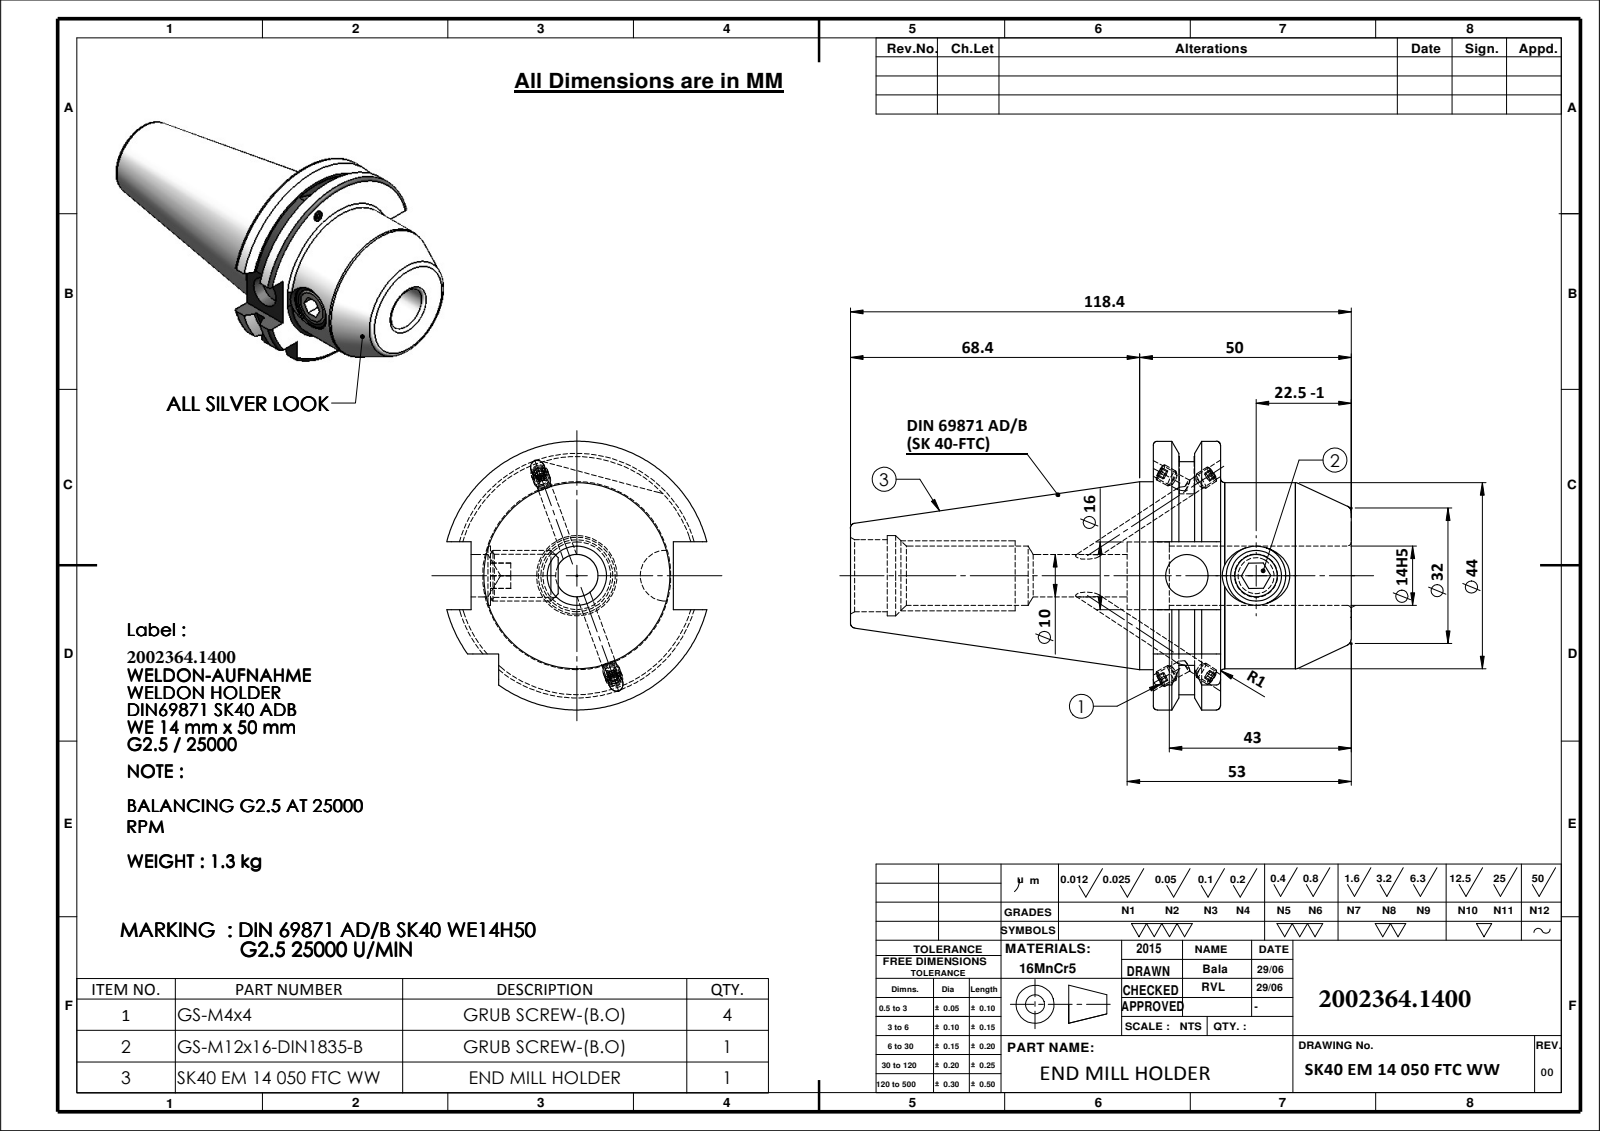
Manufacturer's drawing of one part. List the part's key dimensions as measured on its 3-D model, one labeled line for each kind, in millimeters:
Part name (STEP PRODUCT): SK40 EM 14 050 FTC WW; 91406-WE7 14050; M12X16_ISO 4026 - M12 x 12-N; Copy of M4X4_DIN 913 - M4 x 4-N
STEP written by: SolidWorks 2009 (CONFIG_CONTROL_DESIGN)
Units: millimetres
Bodies: 6 solids, 193 faces (70 planar, 52 cylindrical, 71 other)
Overall size (bounding box): 118.4 × 63.55 × 61.48
Volume: 136 331 mm³ · Surface area: 27 890 mm²
Round holes (diameter × count): ⌀3.3 ×4, ⌀10 ×2, ⌀14 ×2, ⌀10.2 ×1, ⌀16 ×1, ⌀17 ×1, ⌀19 ×1
Round bosses / shafts (diameter × count): ⌀4 ×4, ⌀44.45 ×1, ⌀44 ×1, ⌀12 ×1
Partial cylindrical surfaces — rounded edges, fillets, slot ends (radius × count): R28.12 ×1, R31.77 ×1
Main face-to-face distances: 15.9, 46.8, 30.9, 16.1, 47.8, 71.6, 87.5, 118.4, 65.4, 6.2
Hole centre spacings: 16.35
